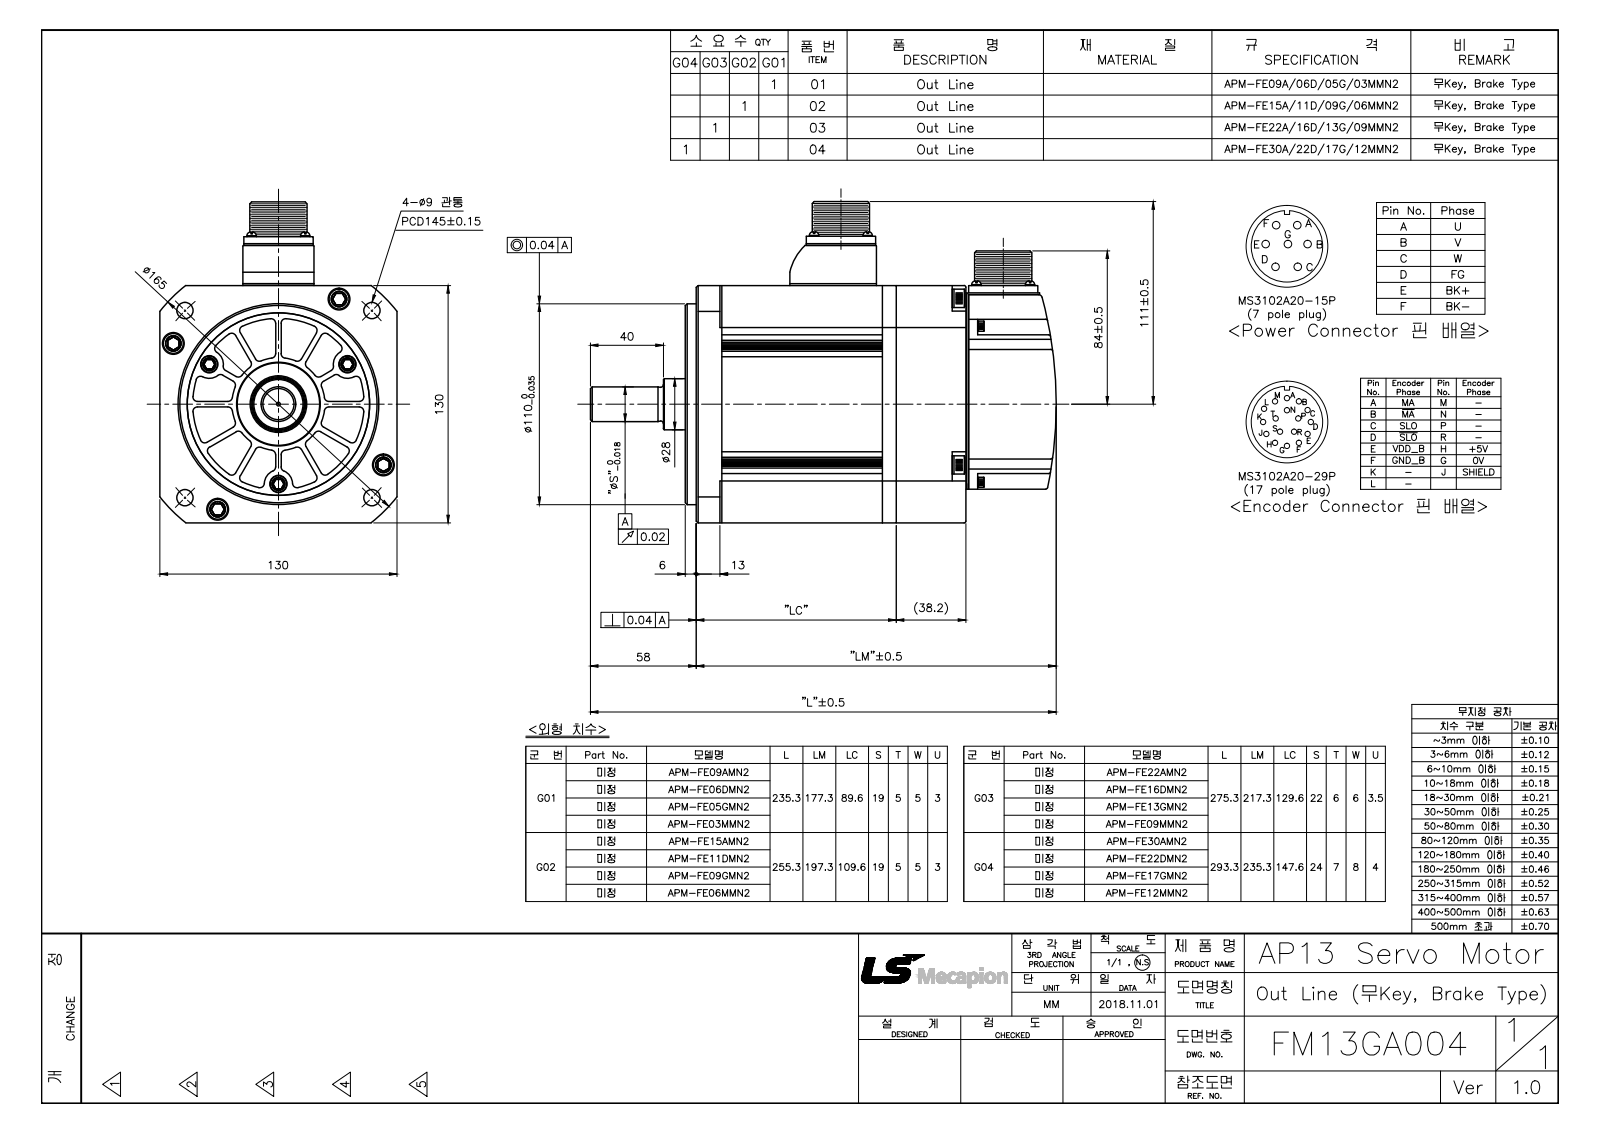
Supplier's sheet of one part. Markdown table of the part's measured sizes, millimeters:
| quantity | value |
| --- | --- |
| part name | FM13GA004G03_Out Line(APM-FE22A_N2,FE16D_N2,FE13G_N2,FE09M_N2) |
| STEP written by | SolidWorks 2011 (AUTOMOTIVE_DESIGN) |
| units | millimeters |
| bodies | 56 solids, 2200 faces (721 planar, 841 cylindrical, 638 other) |
| overall size | 275.3 × 176.05 × 130 |
| volume | 2 990 000 mm³ |
| surface area | 354 289 mm² |
| round holes (diameter × count) | 2.5 × 12, 3 × 8, 3.05 × 8, 3.5 × 8, 5 × 7, 3.6 × 4, 3.7 × 4, 6.8 × 4, 7 × 4, 9 × 4, 11.5 × 4, 5.6 × 3 |
| round bosses / shafts (diameter × count) | 1.6 × 17, 5.4 × 8, 2.4 × 7, 10.2 × 4, 10 × 4, 6 × 4, 5.5 × 4, 3 × 4 |
| partial cylindrical surfaces (radius × count) | 0.5 × 72, 2.5 × 54, 0.7 × 24, 1 × 22, 2 × 17, 3 × 16, 4.5 × 12, 4 × 8 |
| main face-to-face distances | 108, 7.6, 115.6, 1, 130, 155.3, 23, 38.7, 46.3, 154.3 |
| hole center spacings | 20.79, 29.4, 89, 19.1, 26.43, 41.58, 43.75, 50.17 |
